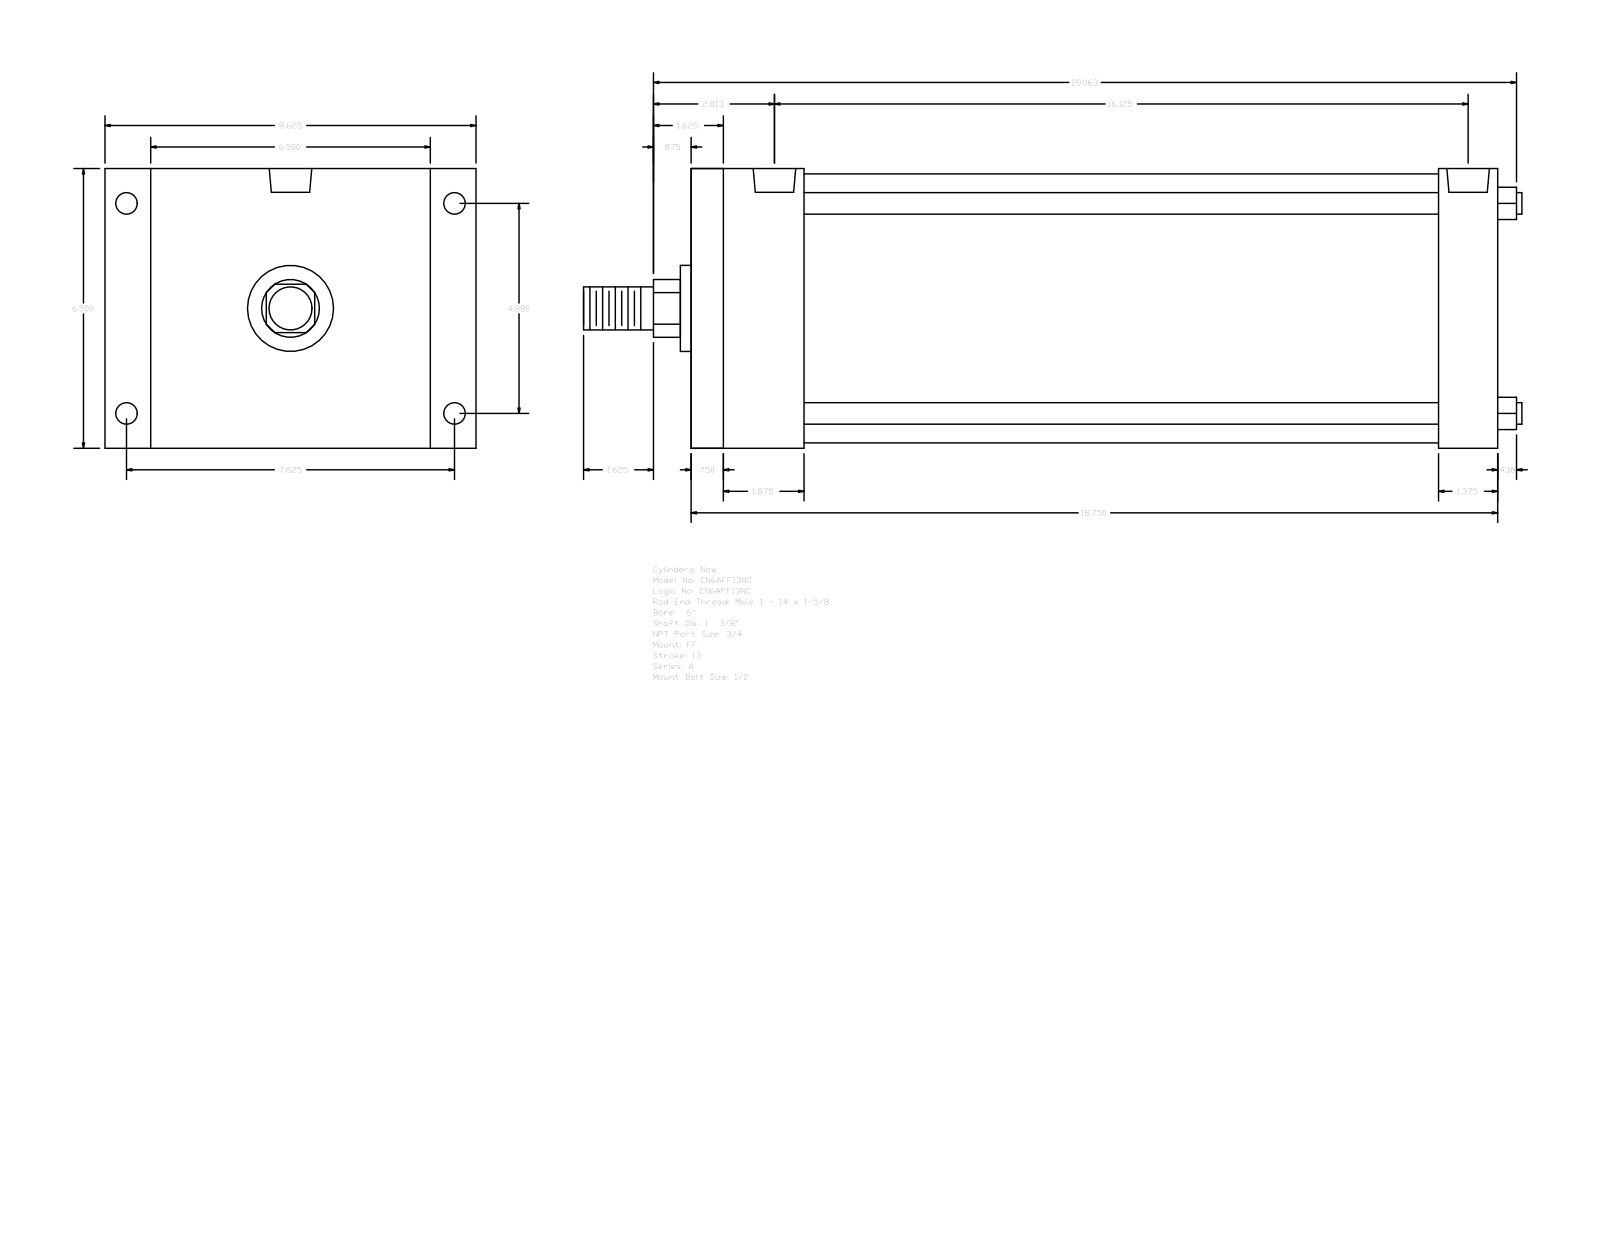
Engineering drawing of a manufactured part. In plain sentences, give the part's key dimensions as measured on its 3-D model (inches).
The part is named "A_FF__0600_1.375". Its 3-D file was written by "GSSL Pune (CONFIG_CONTROL_DESIGN)". It is 0 solids with 92 faces: 64 planar, 28 cylindrical and 0 other. Overall it measures 21.813 by 8.625 by 6.5 inches. Round holes: 4 of diameter 0.5, 4 of diameter 0.594, 2 of diameter 0.989. Round bosses or shafts: 4 of diameter 0.5, 1 of diameter 6.25, 1 of diameter 2, 1 of diameter 1.375, 1 of diameter 1. Partial cylindrical surfaces (rounded edges, fillets, slot ends): 1 of radius 0.672. The main face-to-face distances are 6.5, 18.75, 0.75, 18, 2.625, 1.875, 16.125, 17.375, 16.625, 14.75. The hole center spacings are 0.219, 4.88, 7.625, 9.053, 15.687, 15.906, 16.125.
